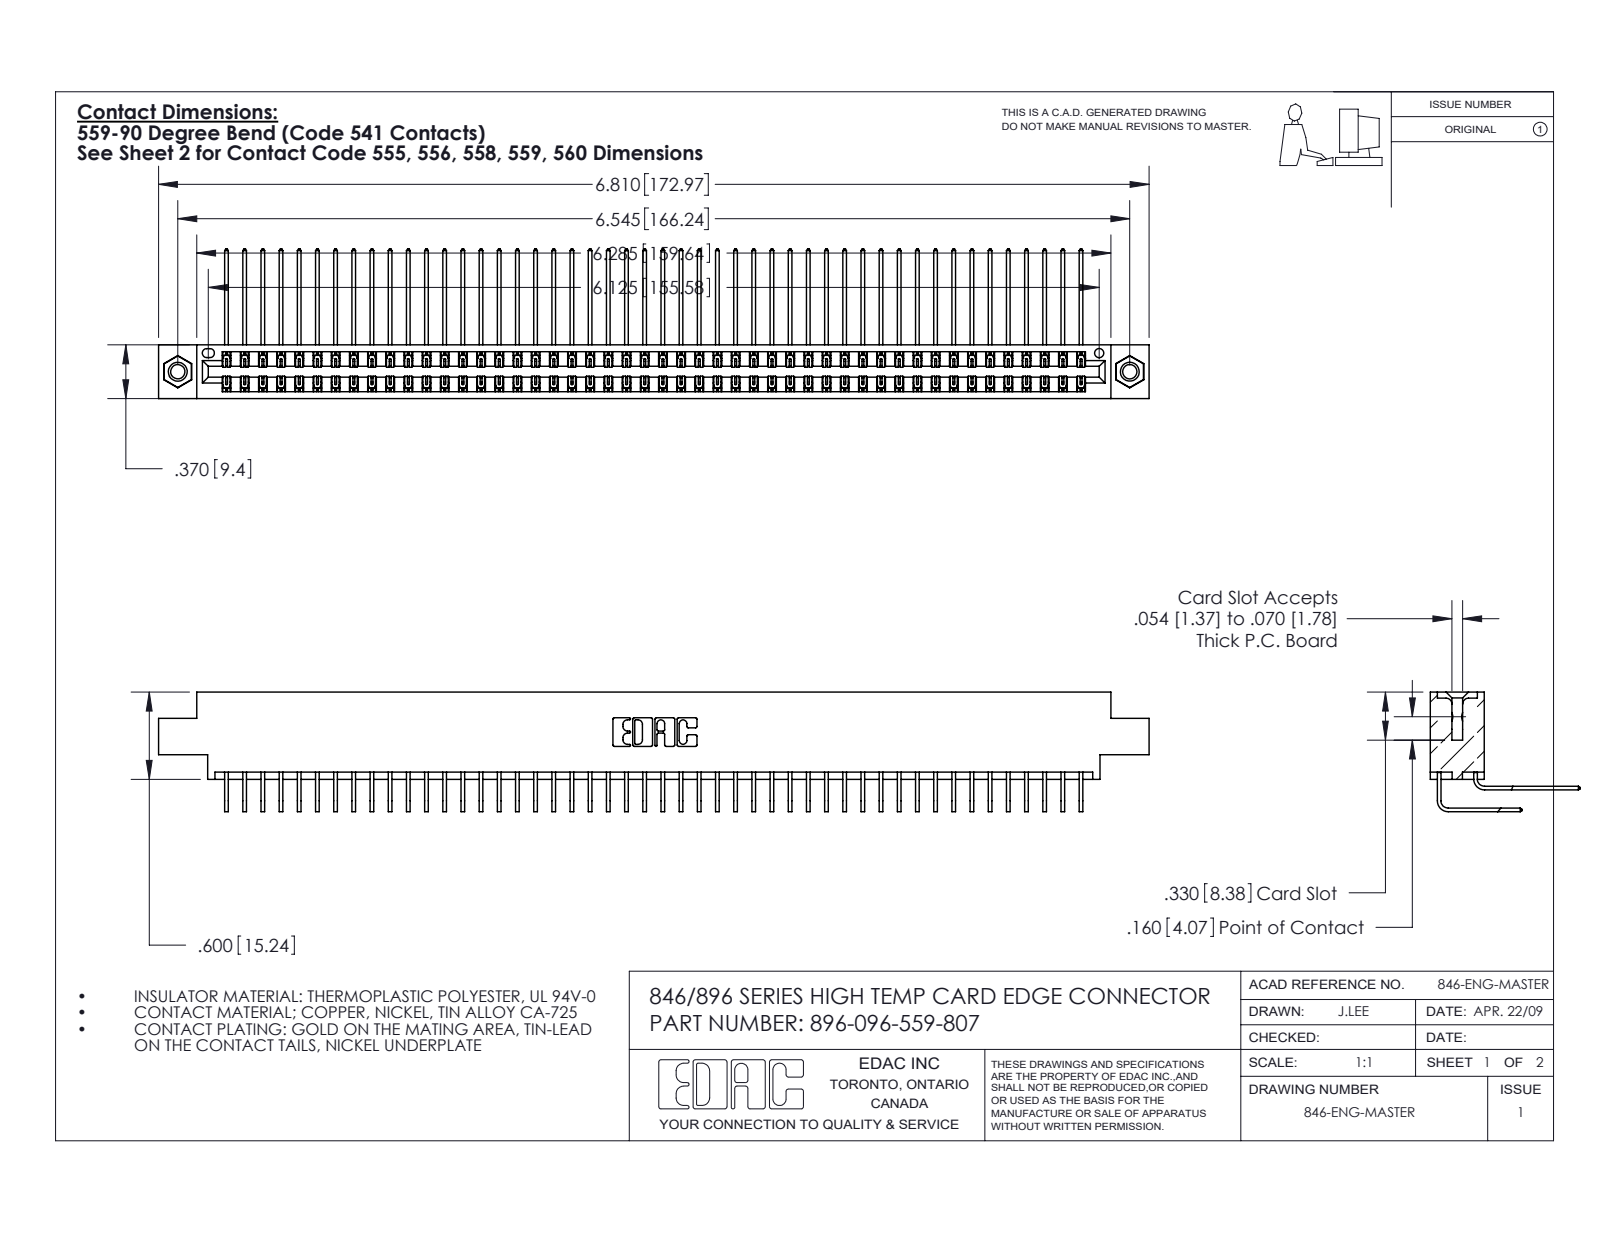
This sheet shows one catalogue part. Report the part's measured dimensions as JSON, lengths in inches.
{"part_name": "345-292-001_559 Tail - 2; 396-096-559-807; 346 Part_0.170 Offset - 0.156 Dia-TI; 345-292-001_558 559 Tail - 1 (+1 more)", "step_written_by": "SolidWorks 2016 (CONFIG_CONTROL_DESIGN)", "units": "inches", "bodies": {"solids": 99, "faces": 5370, "planar": 3664, "cylindrical": 1690, "other": 16}, "overall_size": [6.81, 1.03, 0.823], "volume_in3": 1.056, "surface_area_in2": 41.45, "round_holes": [[0.098, 2], [0.125, 2], [0.156, 2], [0.064, 1]], "round_bosses_or_shafts": [[0.155, 2]], "partial_cylinders_radius": [[0.006, 144], [0.01, 22], [0.007, 6], [0.031, 6], [0.026, 3], [0.014, 2], [0.022, 2], [0.024, 2]], "face_to_face_distances": [0.048, 0.322, 0.025, 0.37, 0.25, 0.072, 0.298, 0.275, 0.222, 0.148], "hole_center_spacings": [0.246, 6.336, 6.545]}
